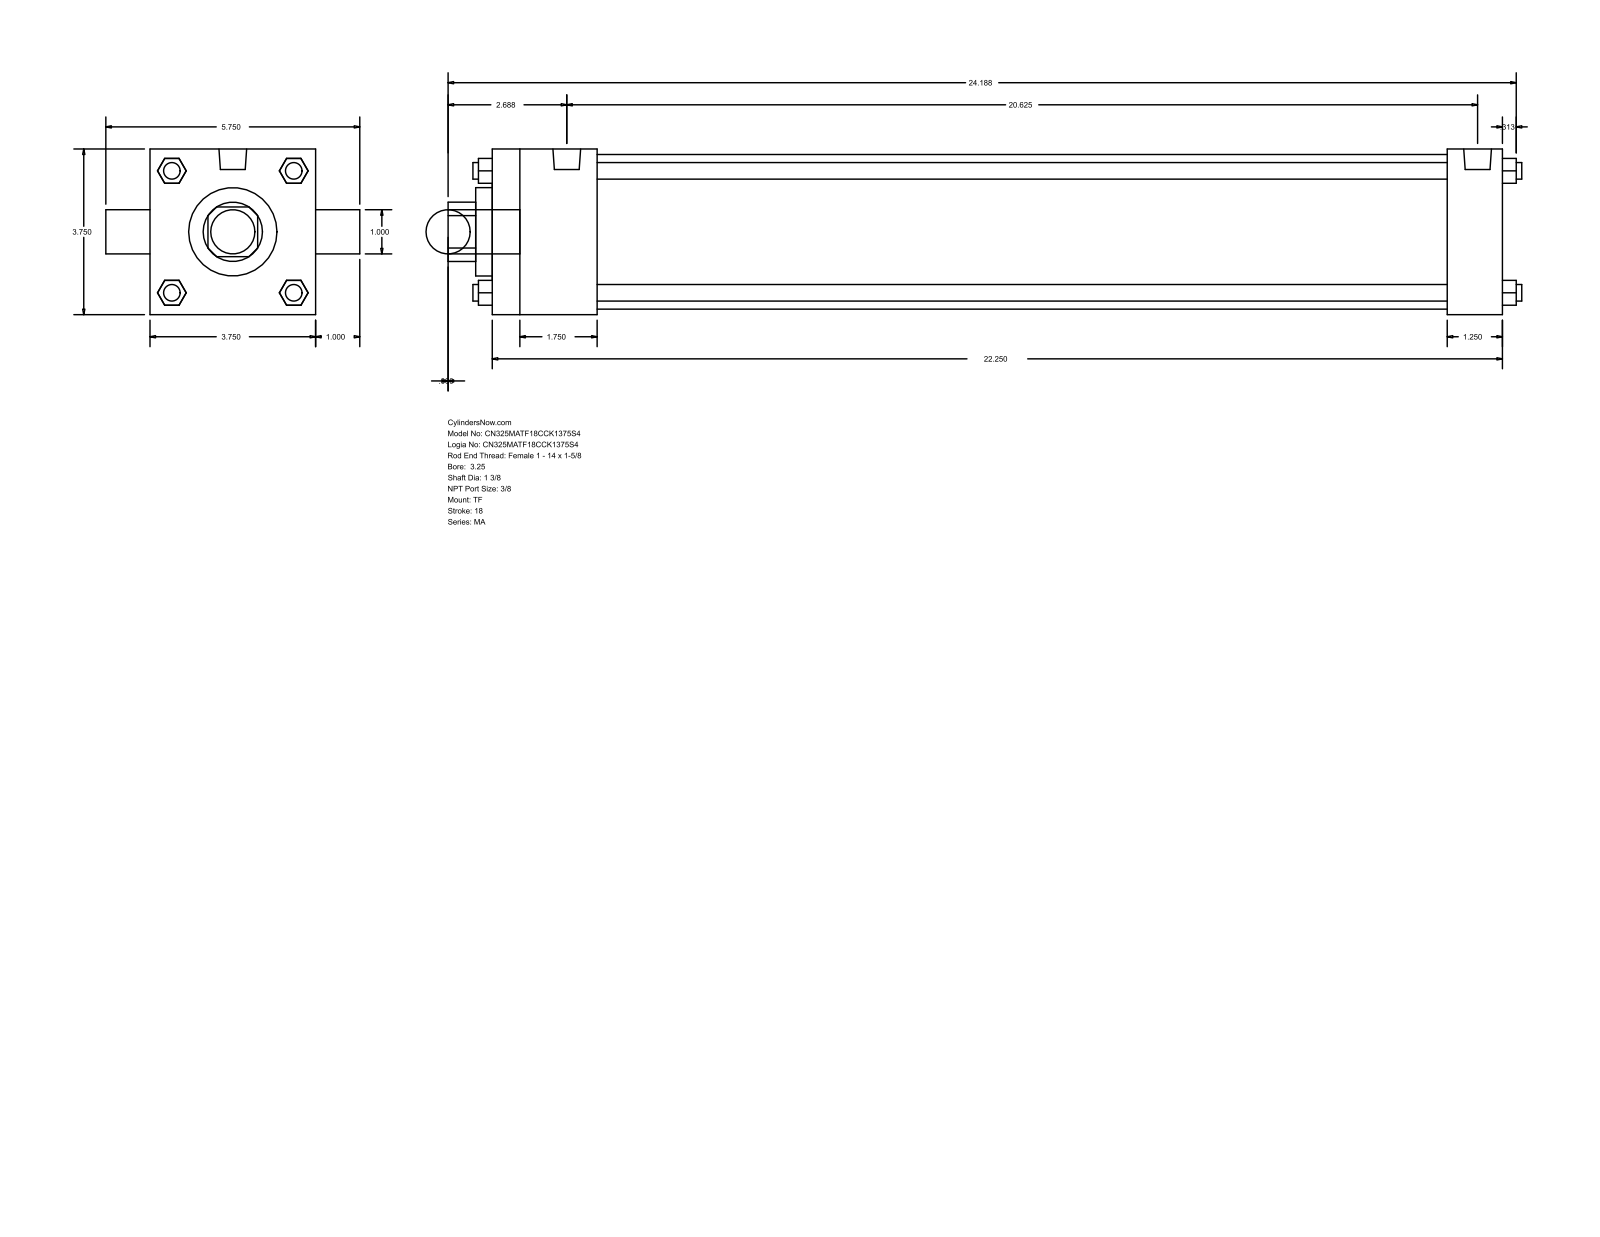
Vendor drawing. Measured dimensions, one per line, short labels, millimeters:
name: MA_TF__0325_1.375
written by: GSSL Pune (CONFIG_CONTROL_DESIGN)
unit: mm
bodies: 0 solids, 120 faces (92 planar, 28 cylindrical, 0 other)
size: 617.54 × 146.05 × 95.25
holes: 1× ⌀25.4, 1× ⌀34.92, 1× ⌀50.8, 1× ⌀88.9
bosses: 4× ⌀9.53, 3× ⌀11.11, 2× ⌀15.93, 1× ⌀25.4
rounds: 1× R17.06
face distances: 95.24, 581.02, 60.32, 549.27, 488.95, 520.7, 31.75, 9.52, 69.84, 558.79
